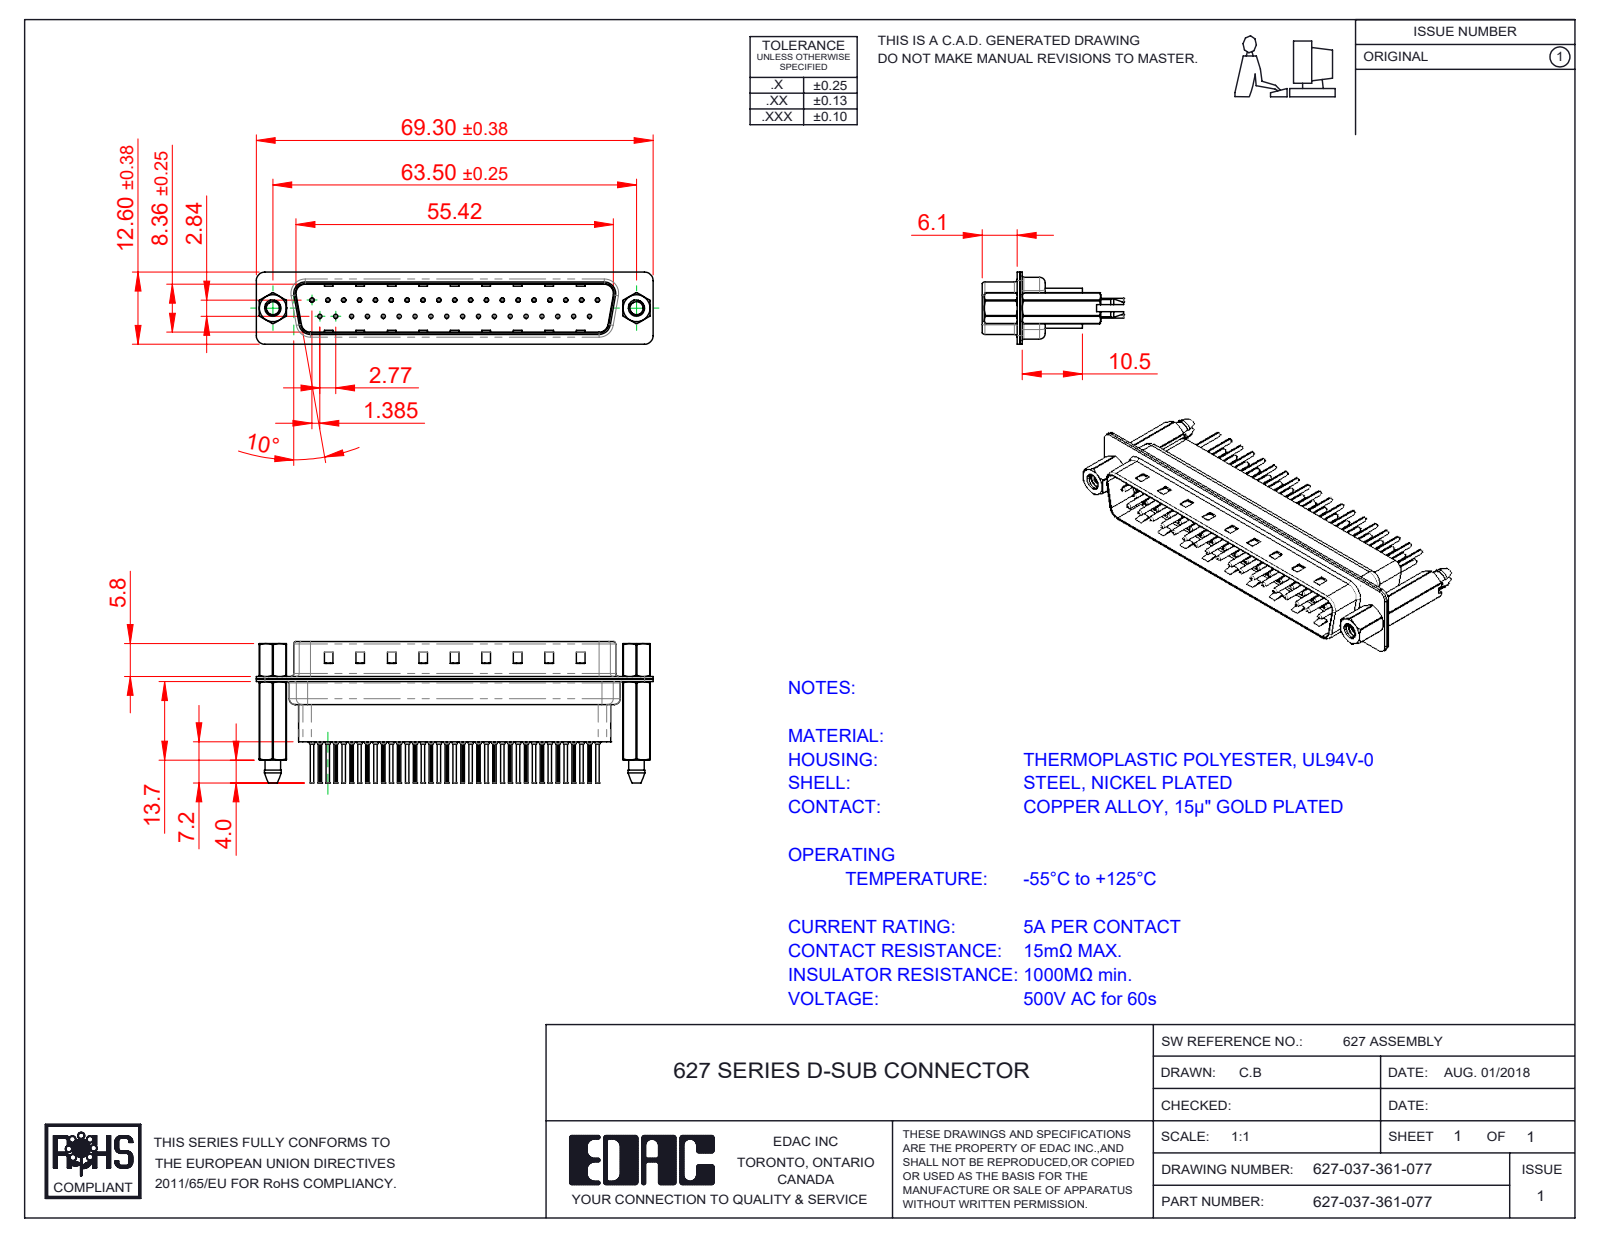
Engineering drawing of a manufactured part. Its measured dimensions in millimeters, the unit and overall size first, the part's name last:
Units: millimetres
Overall size (bounding box): 69.3 × 24.6 × 12.6
Round holes (diameter × count): ⌀0.2 ×37, ⌀0.35 ×37, ⌀1.1 ×37, ⌀1.6 ×37, ⌀2.26 ×2, ⌀2.29 ×2, ⌀4 ×2, ⌀4.8 ×2
Round bosses / shafts (diameter × count): ⌀2 ×37, ⌀1.5 ×37, ⌀0.75 ×37, ⌀0.6 ×37, ⌀4.9 ×2, ⌀2.79 ×2
Partial cylindrical surfaces — rounded edges, fillets, slot ends (radius × count): R0.1 ×74, R1.5 ×18, R2 ×12, R1.6 ×10, R0.5 ×8, R0.25 ×4, R0.6 ×4, R0.65 ×4
Main face-to-face distances: 0.4, 0.82, 9.58, 0.45, 0.68, 7.68, 1.5, 1.08, 8.08, 8.76
Hole centre spacings: 3.16, 2.77, 5.54, 8.31, 5.04, 10.1, 11.08, 12.78
Volume: 5 896 mm³ · Surface area: 15 166 mm²
Bodies: 44 solids, 4272 faces (1145 planar, 1648 cylindrical, 1479 other)
Part name (STEP PRODUCT): 627 Shell Rear_37 Contacts; 627 4-40 Threaded Boardlock_HP61; 627 Housing_37 HP; 627 Shell Front_37 Contacts (+4 more)
STEP written by: SolidWorks 2020 (CONFIG_CONTROL_DESIGN)
